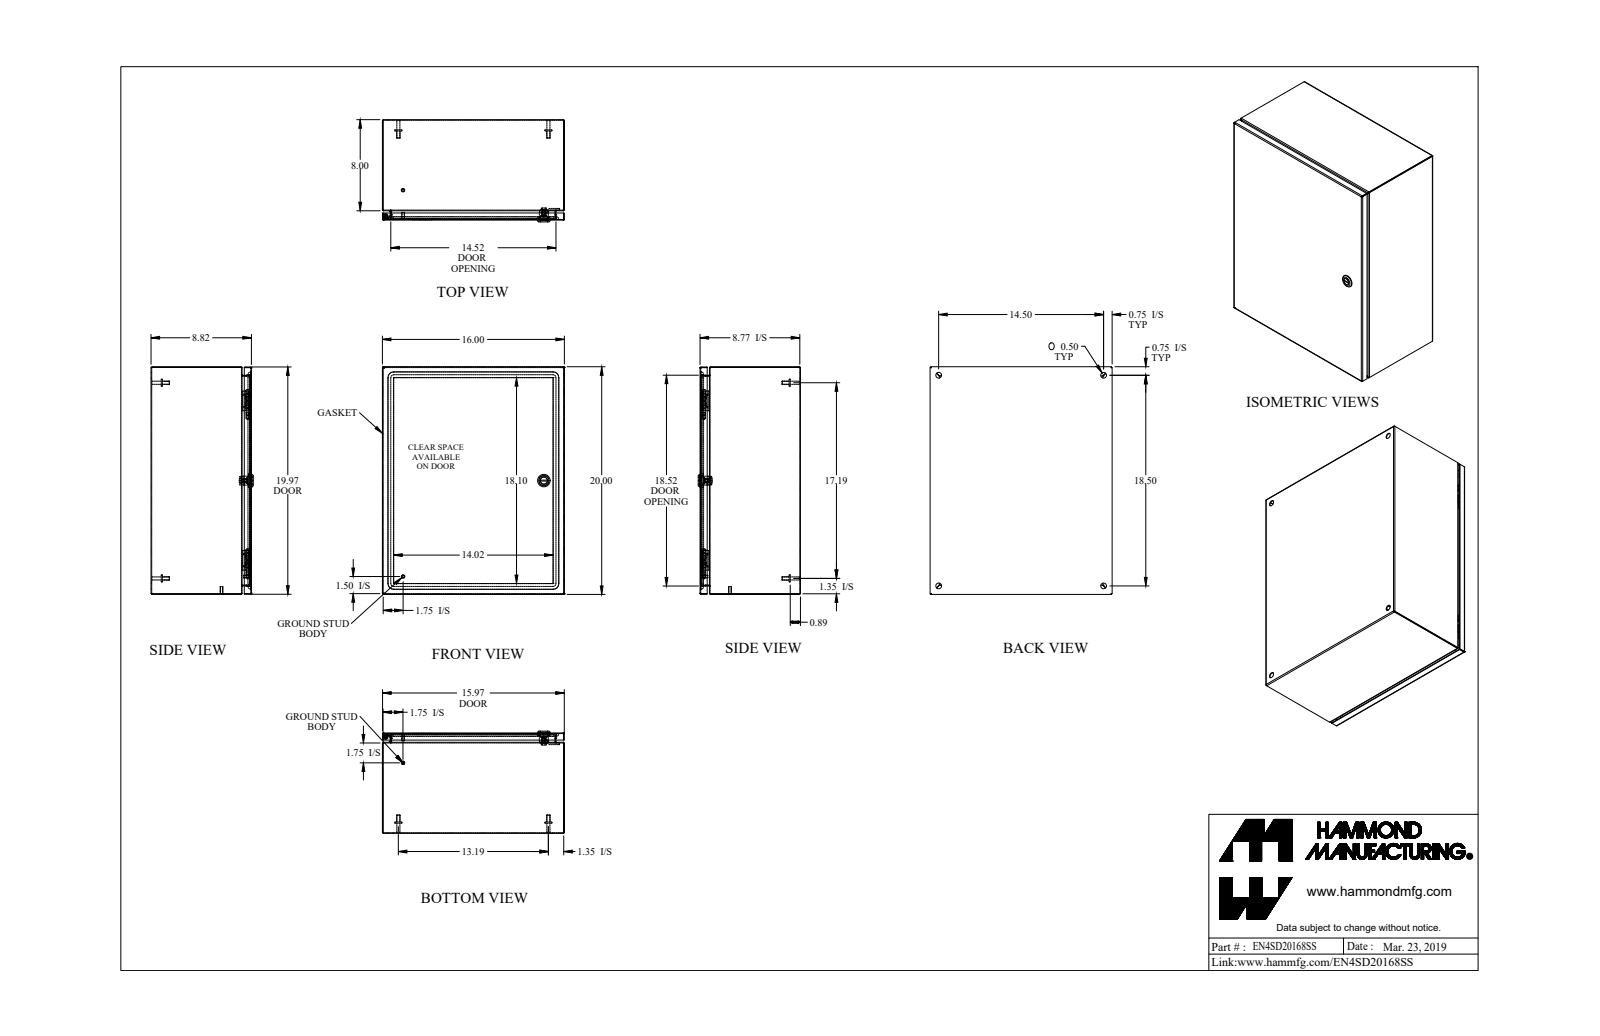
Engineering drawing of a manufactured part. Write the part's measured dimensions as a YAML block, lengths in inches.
part_name: "EN4SD20168SS_Default"
step_written_by: "SolidWorks 2019 (CONFIG_CONTROL_DESIGN)"
units: inches
bodies: {solids: 22, faces: 657, planar: 303, cylindrical: 212, other: 142}
overall_size: [20, 16, 8.982]
volume: 84.47
surface_area: 2876
round_holes:
  - {diameter: 0.5, count: 5}
  - {diameter: 0.172, count: 1}
  - {diameter: 0.197, count: 1}
  - {diameter: 0.24, count: 1}
  - {diameter: 0.242, count: 1}
  - {diameter: 0.387, count: 1}
  - {diameter: 0.63, count: 1}
  - {diameter: 0.768, count: 1}
round_bosses_or_shafts:
  - {diameter: 0.313, count: 6}
  - {diameter: 0.625, count: 4}
  - {diameter: 0.275, count: 4}
  - {diameter: 0.25, count: 2}
  - {diameter: 1.1, count: 1}
  - {diameter: 0.785, count: 1}
  - {diameter: 0.625, count: 1}
  - {diameter: 0.525, count: 1}
partial_cylinders:
  - {radius: 0.029, count: 21}
  - {radius: 0.086, count: 21}
  - {radius: 0.188, count: 12}
  - {radius: 0.006, count: 4}
  - {radius: 0.062, count: 4}
  - {radius: 0.25, count: 4}
  - {radius: 0.499, count: 4}
  - {radius: 0.125, count: 2}
face_to_face_distances: [0.057, 8.765, 8.708, 8.822, 15.943, 19.943, 15.886, 16, 19.886, 20]
hole_center_spacings: [9.31, 14.5, 16.316, 18.5, 23.506]
